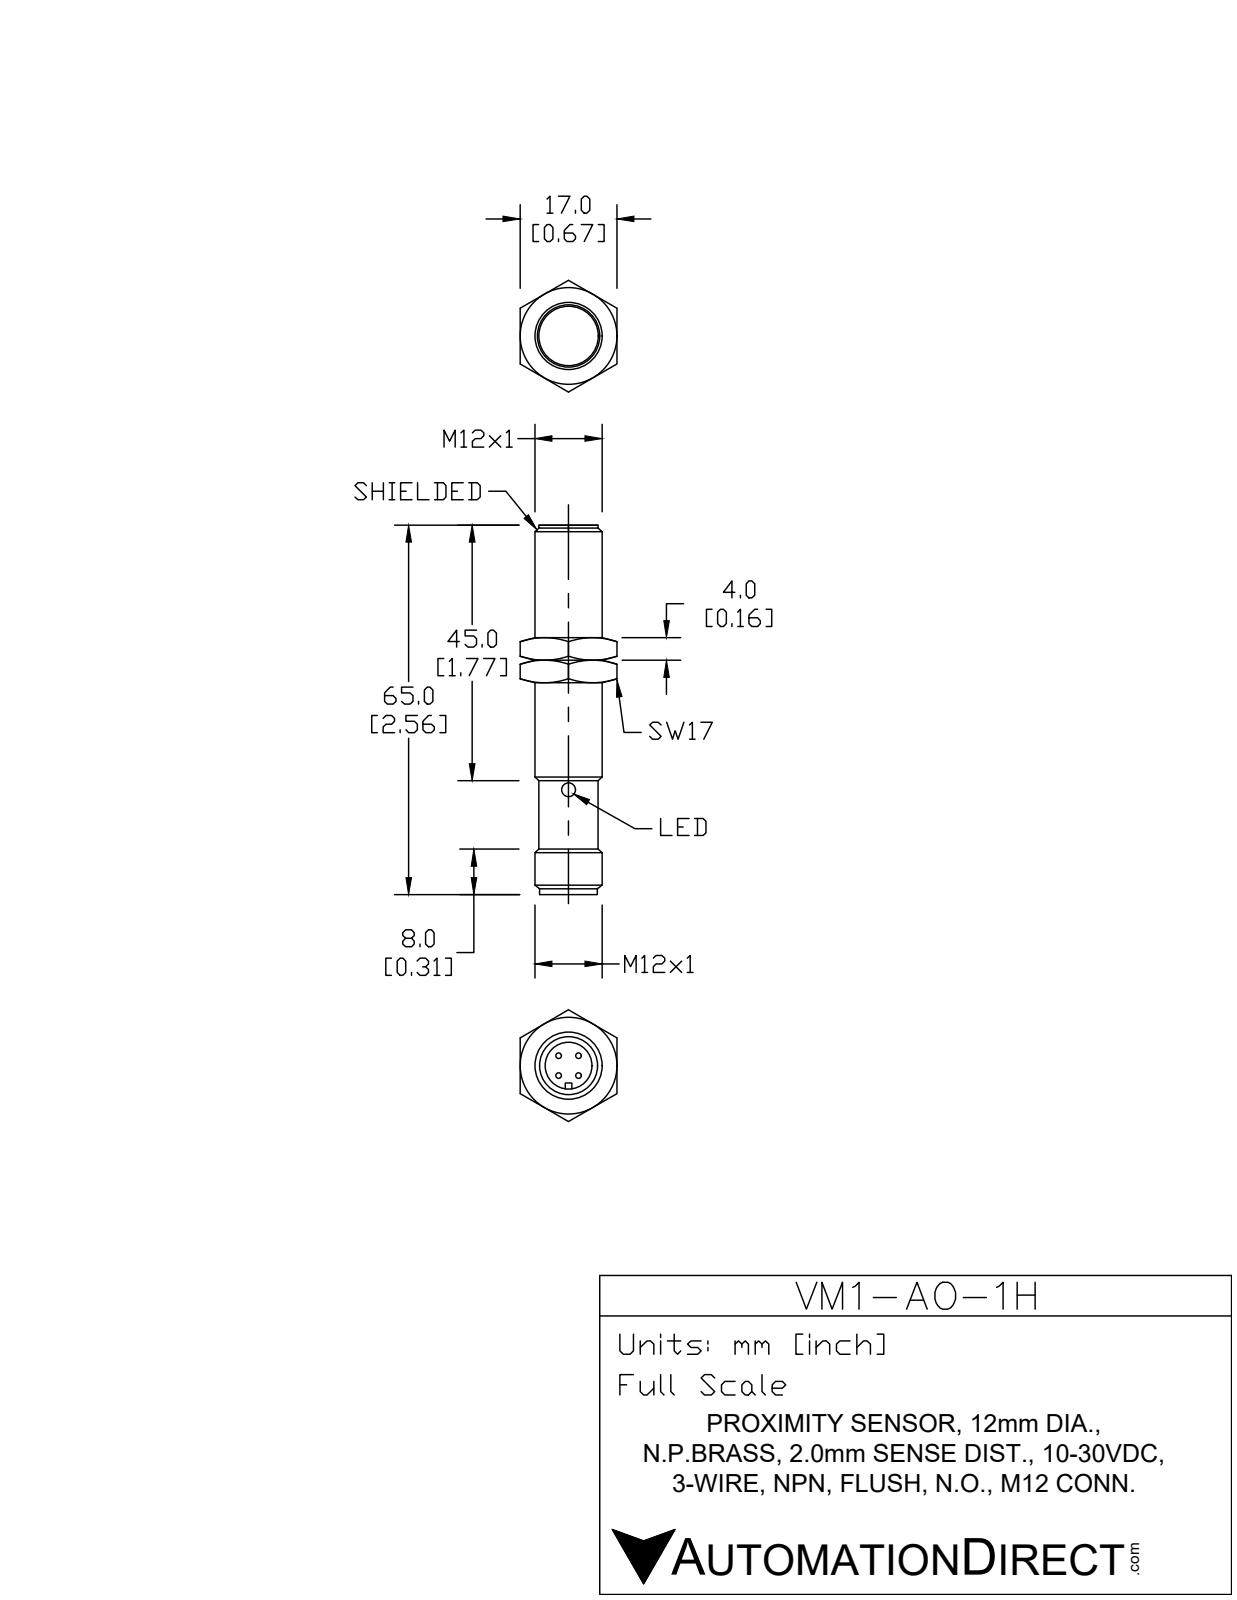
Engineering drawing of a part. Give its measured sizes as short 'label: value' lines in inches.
name: VM1-A0-1H
written by: SolidWorks 2017 (AUTOMOTIVE_DESIGN)
unit: in
bodies: 3 solids, 99 faces (22 planar, 51 cylindrical, 26 other)
size: 2.559 × 0.472 × 0.472
volume: 0.374 in³; area: 6.343 in²
holes: 1× ⌀0.098, 1× ⌀0.331, 1× ⌀0.374
bosses: 4× ⌀0.039, 1× ⌀0.472, 1× ⌀0.413, 1× ⌀0.382, 1× ⌀0.378
rounds: 4× R0.051, 1× R0.02, 1× R0.024, 1× R0.051, 1× R0.134
face distances: 0.02, 2.122, 2.102, 1.97, 1.95, 0.152, 2.52, 2.5, 0.55, 0.398
